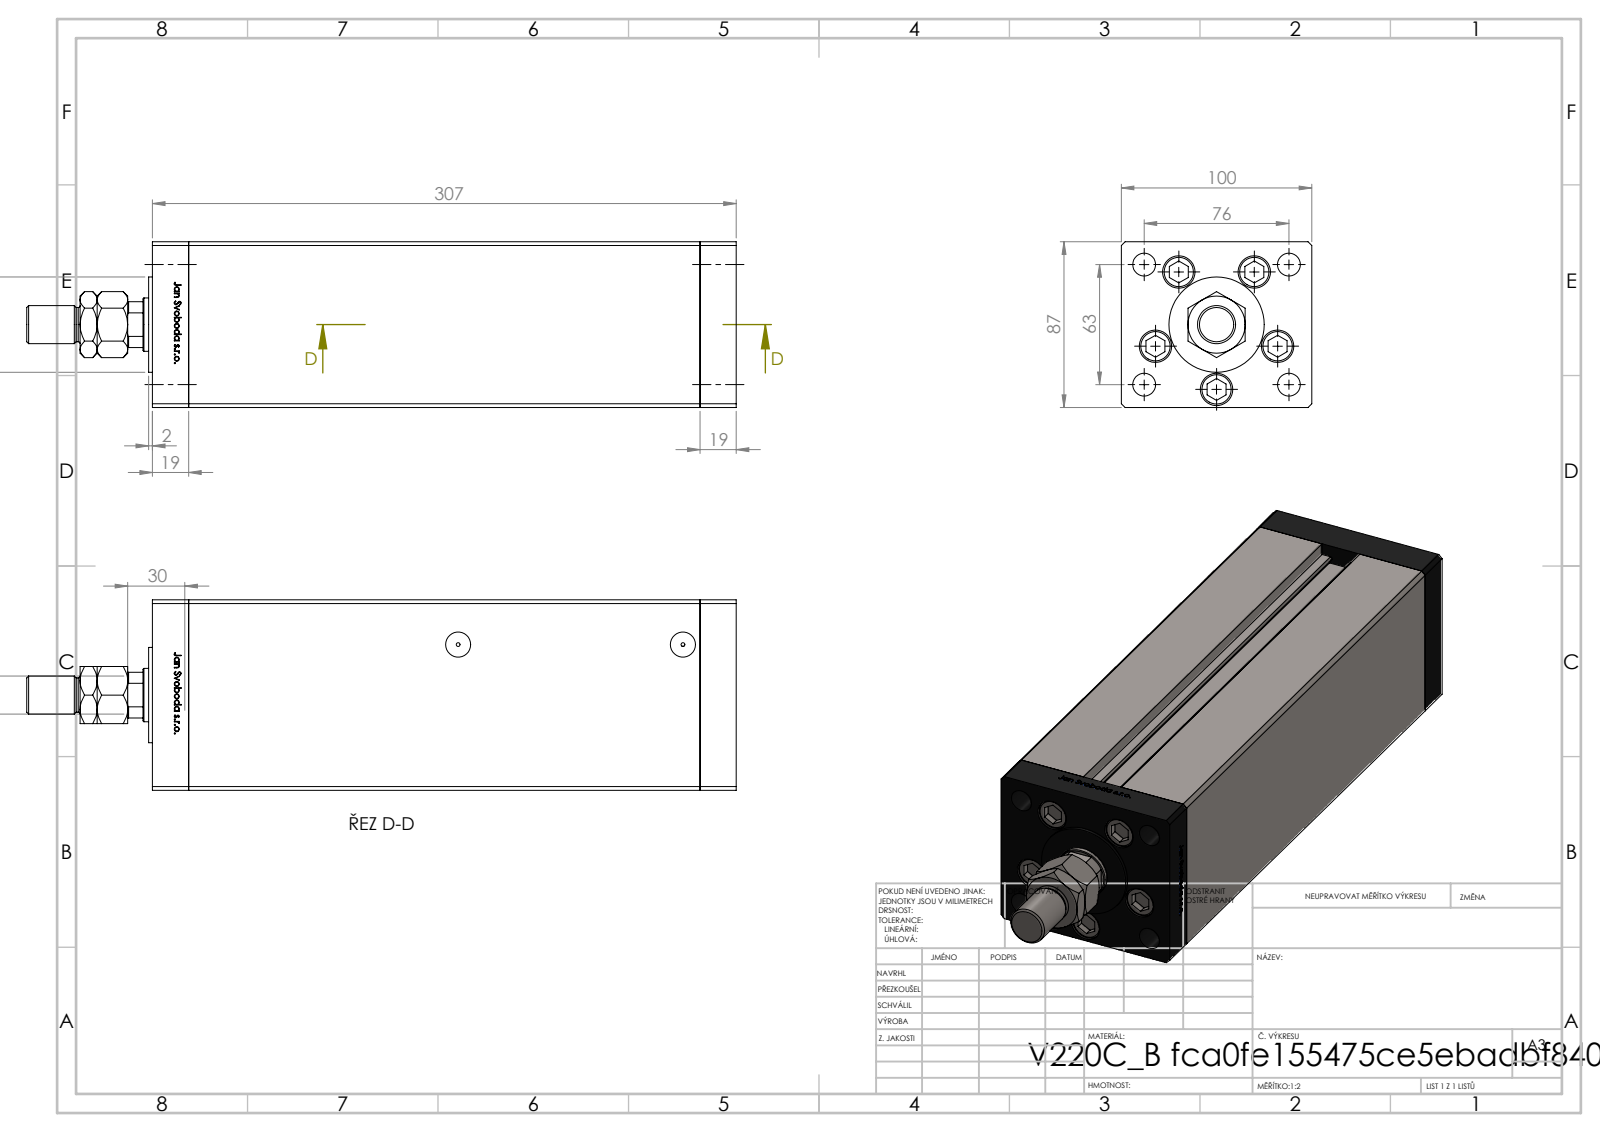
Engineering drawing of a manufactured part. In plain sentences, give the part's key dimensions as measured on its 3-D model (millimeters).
The part is named "V220C_B MIDDLE; MTA; ALLEN BOLT; V220C BACK_B (+2 more)". Its 3-D file was written by "SolidWorks 2019 (CONFIG_CONTROL_DESIGN)". It is 15 solids with 1234 faces: 479 planar, 151 cylindrical and 604 other. Overall it measures 372.5 by 100 by 87 millimeters. Its volume is 2 318 000 cubic millimeters and its surface area 287 838 square millimeters. Round holes: 7 of diameter 13.5, 5 of diameter 17, 4 of diameter 12, 2 of diameter 2, 2 of diameter 13.16, 1 of diameter 18.5, 1 of diameter 28. Round bosses or shafts: 5 of diameter 8, 2 of diameter 17, 1 of diameter 50, 1 of diameter 20, 1 of diameter 18. Partial cylindrical surfaces (rounded edges, fillets, slot ends): 2 of radius 0.93, 1 of radius 13.5. The main face-to-face distances are 100, 87, 19, 268.5, 287.5, 34.25, 306.5, 15.25, 253.25, 272.25. The hole center spacings are 34, 18.59, 39.64, 49.36, 57.95, 21.03, 38.08, 39.27.
